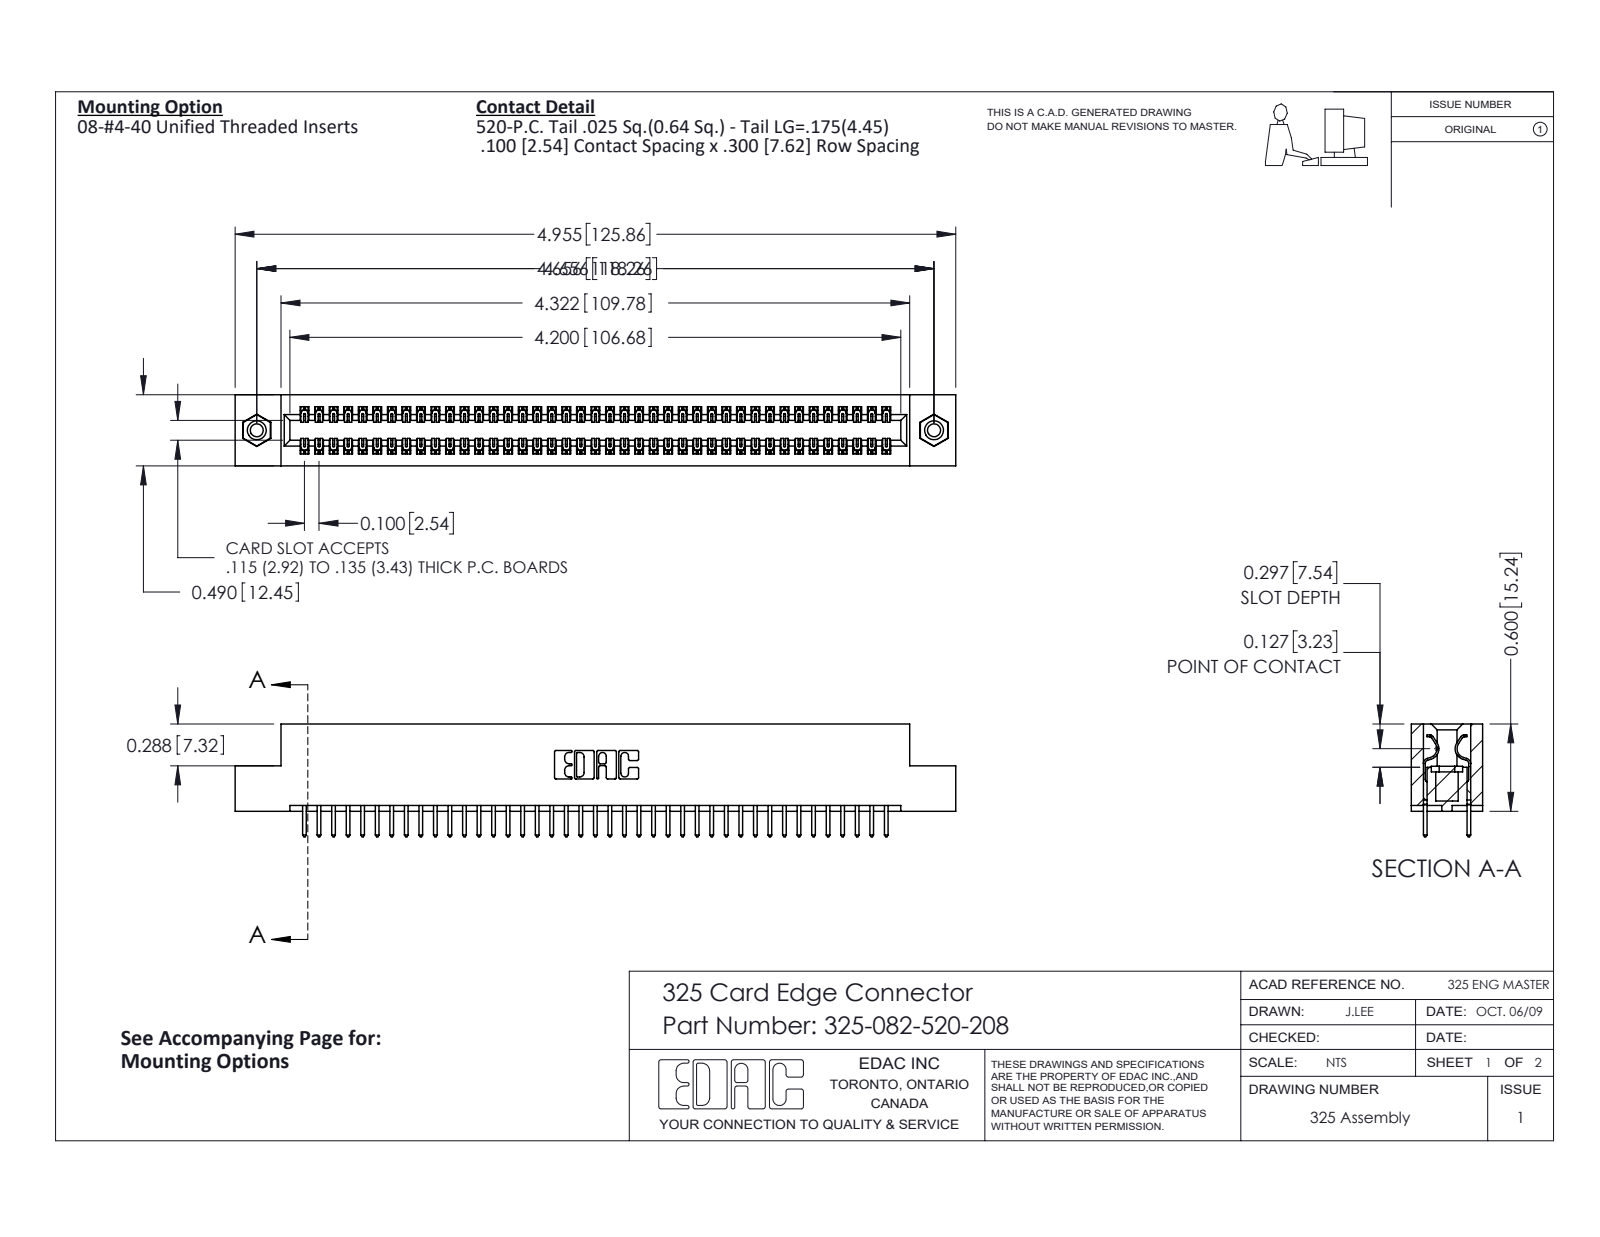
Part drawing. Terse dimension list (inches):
name: 325-292-001_325-293-120; 345-250-001_345-250-003-102; 325-082-520-208; 325 Part_TI
written by: SolidWorks 2016 (CONFIG_CONTROL_DESIGN)
unit: in
bodies: 85 solids, 4438 faces (3054 planar, 1368 cylindrical, 16 other)
size: 4.955 × 0.775 × 0.49
volume: 0.99 in³; area: 30.16 in²
holes: 2× ⌀0.089, 2× ⌀0.125, 2× ⌀0.16
bosses: 2× ⌀0.155
rounds: 123× R0.006, 82× R0.01, 22× R0.01, 6× R0.007, 6× R0.031, 3× R0.026, 2× R0.014, 2× R0.022
face distances: 0.083, 0.407, 0.3, 0.49, 0.107, 0.383, 0.025, 0.325, 0.275, 0.56
hole spacings: 4.656
